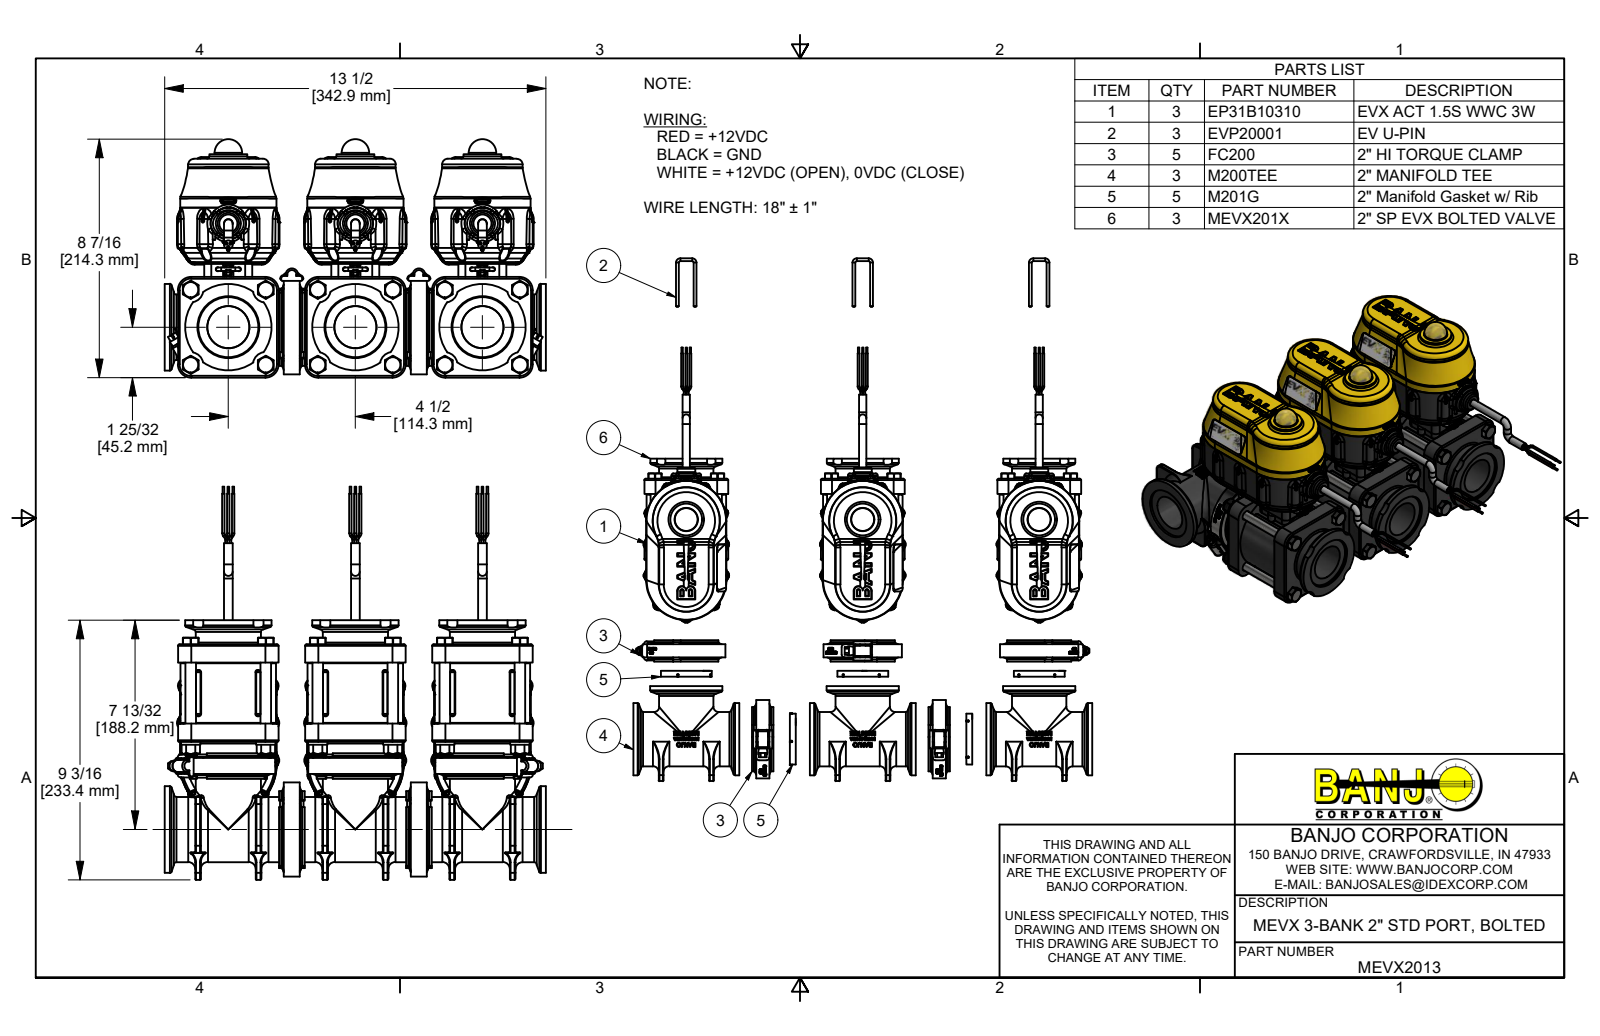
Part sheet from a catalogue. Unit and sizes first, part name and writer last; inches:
Units: inches
Overall size (bounding box): 13.914 × 13.5 × 8.437
Round holes (diameter × count): ⌀0.095 ×33, ⌀0.15 ×33, ⌀0.08 ×21, ⌀0.107 ×12, ⌀0.126 ×12, ⌀0.136 ×12, ⌀0.148 ×12, ⌀0.15 ×12, ⌀0.17 ×12, ⌀0.307 ×12, ⌀0.385 ×12, ⌀0.406 ×12
Round bosses / shafts (diameter × count): ⌀0.324 ×180, ⌀0.25 ×51, ⌀0.08 ×45, ⌀0.14 ×33, ⌀0.108 ×33, ⌀0.085 ×33, ⌀0.058 ×18, ⌀0.375 ×15
Partial cylindrical surfaces — rounded edges, fillets, slot ends (radius × count): R0.013 ×540, R0.04 ×435, R0.01 ×234, R0.02 ×198, R0.03 ×188, R0.005 ×135, R0.06 ×101, R0.08 ×84
Main face-to-face distances: 0.1, 4.5, 0.85, 4.308, 2.565, 0.06, 9, 3.658, 3.483, 0.65
Hole centre spacings: 4.5, 4.778, 9, 1.662, 2.088, 2.656, 2.69, 2.715
Volume: 252 in³ · Surface area: 2 455 in²
Bodies: 301 solids, 36503 faces (9616 planar, 10547 cylindrical, 16340 other)
Part name (STEP PRODUCT): MEVX2013; EP31B10310; B61905PPHS; B632038PM (+8 more)
STEP written by: Autodesk Inventor 2019 (AUTOMOTIVE_DESIGN)
